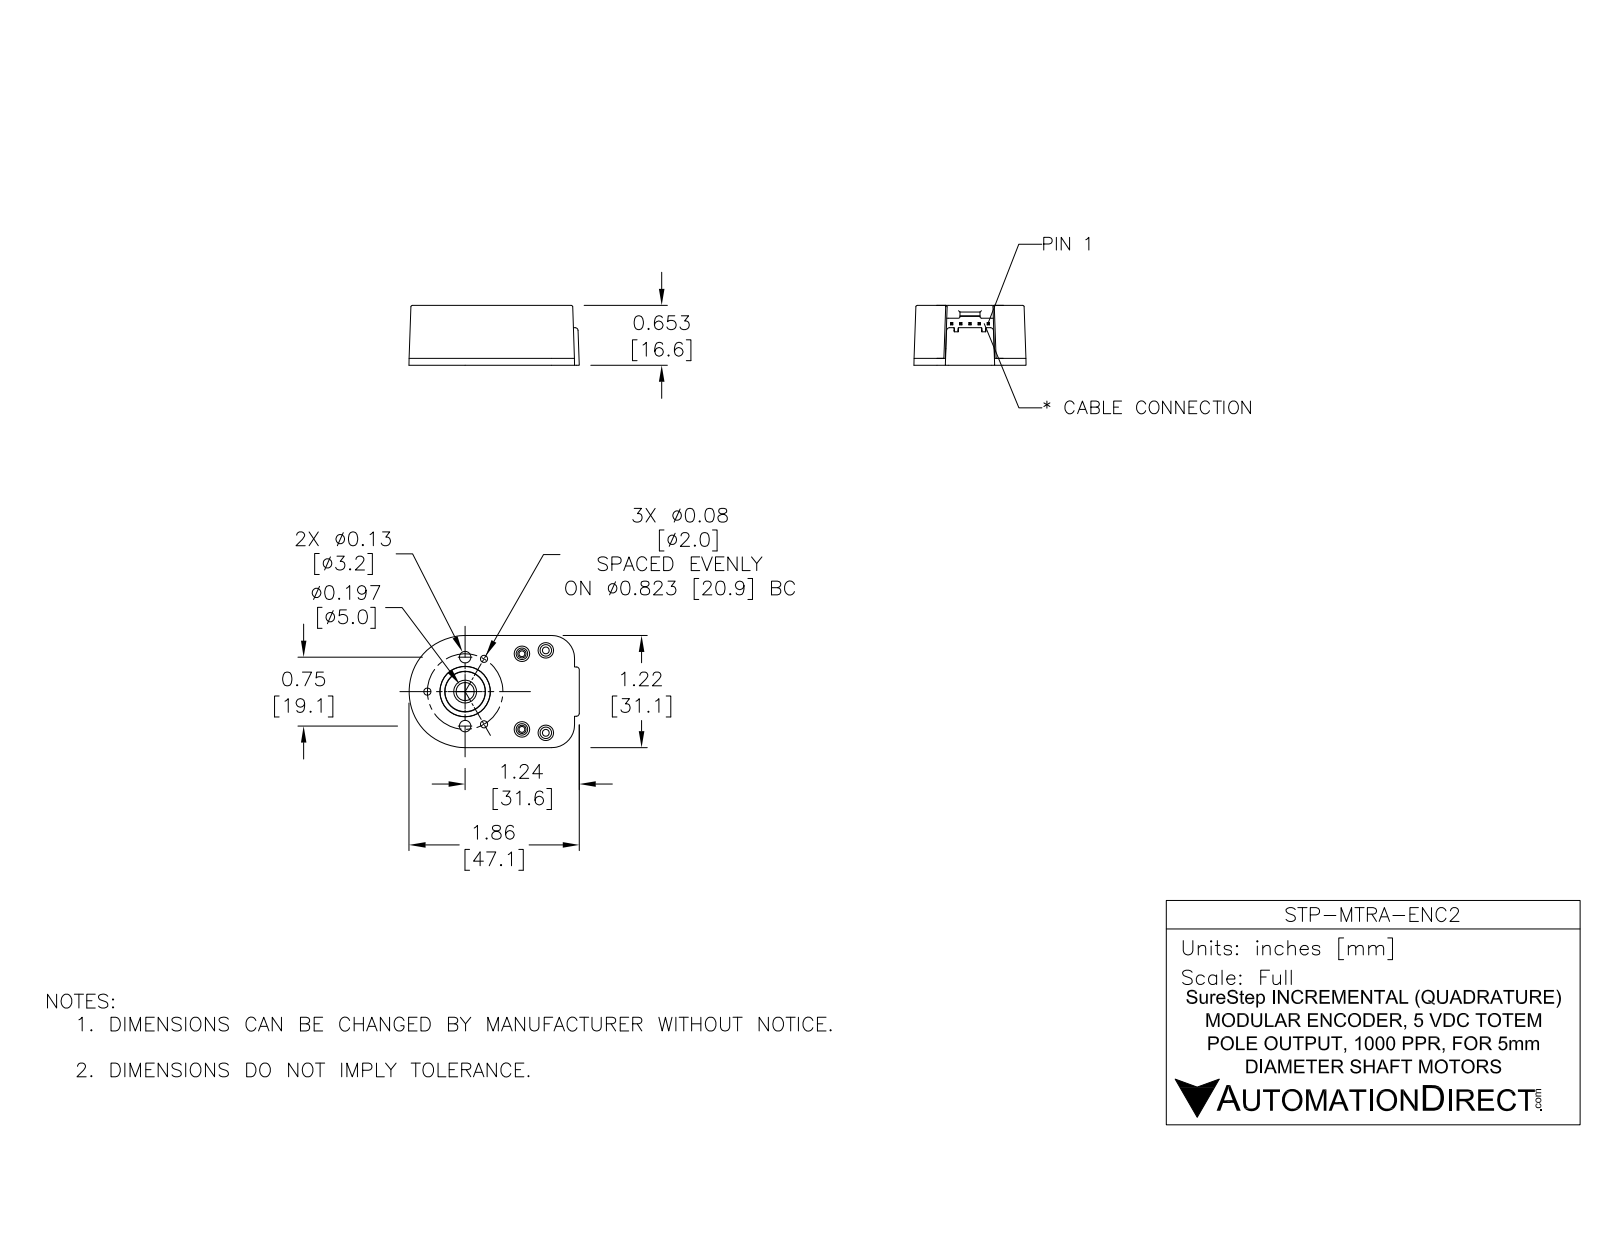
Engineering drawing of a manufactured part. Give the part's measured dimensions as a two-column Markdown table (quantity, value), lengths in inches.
| quantity | value |
| --- | --- |
| part name | ENC2 |
| STEP written by | SolidWorks 2017 (AUTOMOTIVE_DESIGN) |
| units | inches |
| bodies | 12 solids, 1154 faces (403 planar, 289 cylindrical, 462 other) |
| overall size | 1.856 × 1.223 × 0.653 |
| volume | 0.474 in³ |
| surface area | 20.27 in² |
| round holes (diameter × count) | 0.089 × 4, 0.078 × 3, 0.145 × 3, 0.095 × 2, 0.109 × 2, 0.125 × 2, 0.093 × 1, 0.145 × 1, 0.197 × 1 |
| round bosses / shafts (diameter × count) | 0.187 × 4, 0.16 × 4, 0.096 × 4, 0.112 × 3, 0.195 × 2, 0.52 × 1, 0.487 × 1, 0.375 × 1 |
| partial cylindrical surfaces (radius × count) | 0.016 × 36, 0.031 × 24, 0.01 × 4, 0.047 × 2, 0.047 × 2, 0.048 × 2, 0.075 × 2, 0.095 × 2 |
| main face-to-face distances | 0.653, 0.135, 0.518, 0.405, 0.54, 0.113, 0.465, 0.075, 0.06, 0.578 |
| hole center spacings | 0.162, 0.207, 0.282, 0.411, 0.418, 0.557, 0.621, 0.7 |
